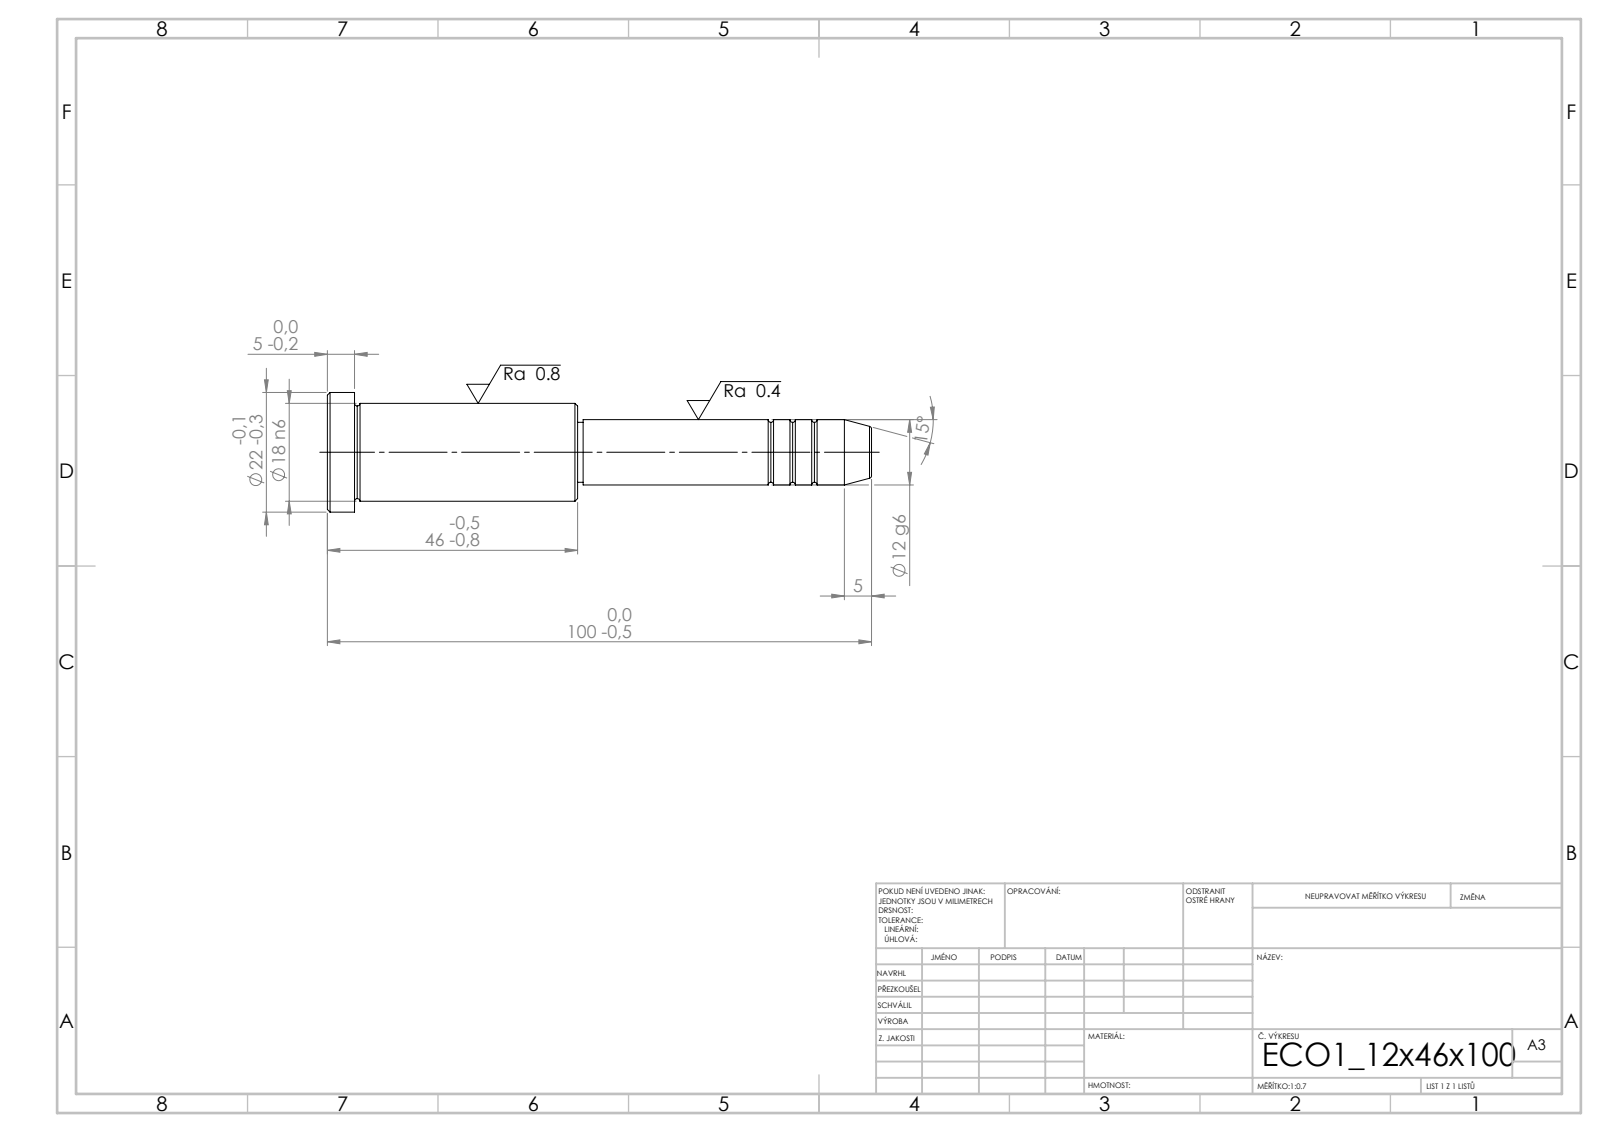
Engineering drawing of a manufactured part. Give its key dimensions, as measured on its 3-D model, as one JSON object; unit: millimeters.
{"step_written_by": "SolidWorks 2019 (CONFIG_CONTROL_DESIGN)", "units": "millimeters", "bodies": {"solids": 1, "faces": 43, "planar": 5, "cylindrical": 14, "other": 24}, "overall_size": [100, 22, 22], "volume_mm3": 18225, "surface_area_mm2": 5476, "round_bosses_or_shafts": [[22, 1], [18, 1], [12, 1], [11, 1]], "face_to_face_distances": [46, 41, 5, 54, 95, 100, 53, 1, 42, 47]}
